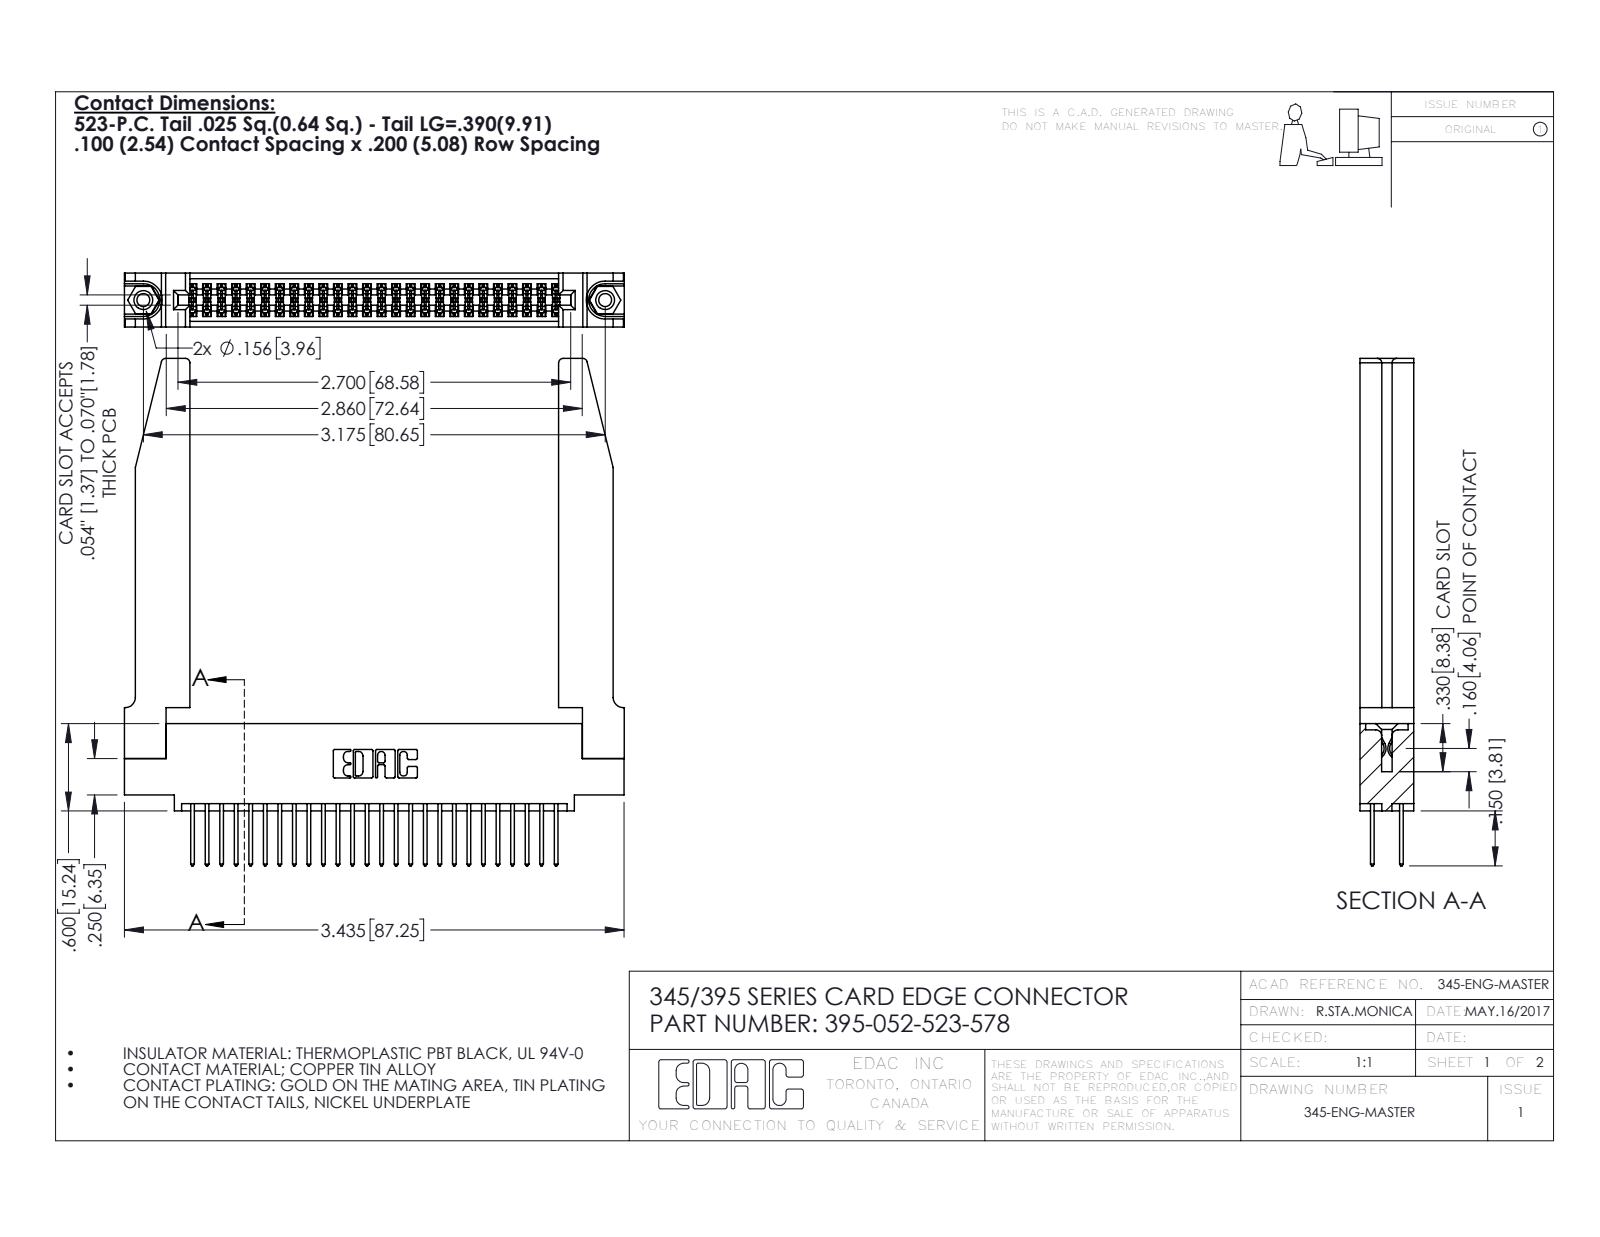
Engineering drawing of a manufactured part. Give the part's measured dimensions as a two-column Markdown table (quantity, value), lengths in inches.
| quantity | value |
| --- | --- |
| part name | 345-250-001_345-250-001-102; 395-052-523-578; 345-220-078_345-220-078; 345-292-001_345-293-123 (+1 more) |
| STEP written by | SolidWorks 2016 (CONFIG_CONTROL_DESIGN) |
| units | inches |
| bodies | 57 solids, 2964 faces (1942 planar, 970 cylindrical, 52 other) |
| overall size | 3.487 × 3.436 × 0.37 |
| volume | 0.985 in³ |
| surface area | 30.16 in² |
| round holes (diameter × count) | 0.089 × 2, 0.125 × 2, 0.156 × 2, 0.064 × 1 |
| round bosses / shafts (diameter × count) | 0.155 × 2 |
| partial cylindrical surfaces (radius × count) | 0.006 × 78, 0.01 × 52, 0.01 × 22, 0.03 × 8, 0.007 × 6, 0.031 × 6, 0.026 × 3, 0.014 × 2 |
| main face-to-face distances | 0.37, 0.072, 0.298, 0.2, 0.098, 0.272, 0.025, 0.225, 0.148, 0.15 |
| hole center spacings | 0.27, 2.94, 3.175 |
